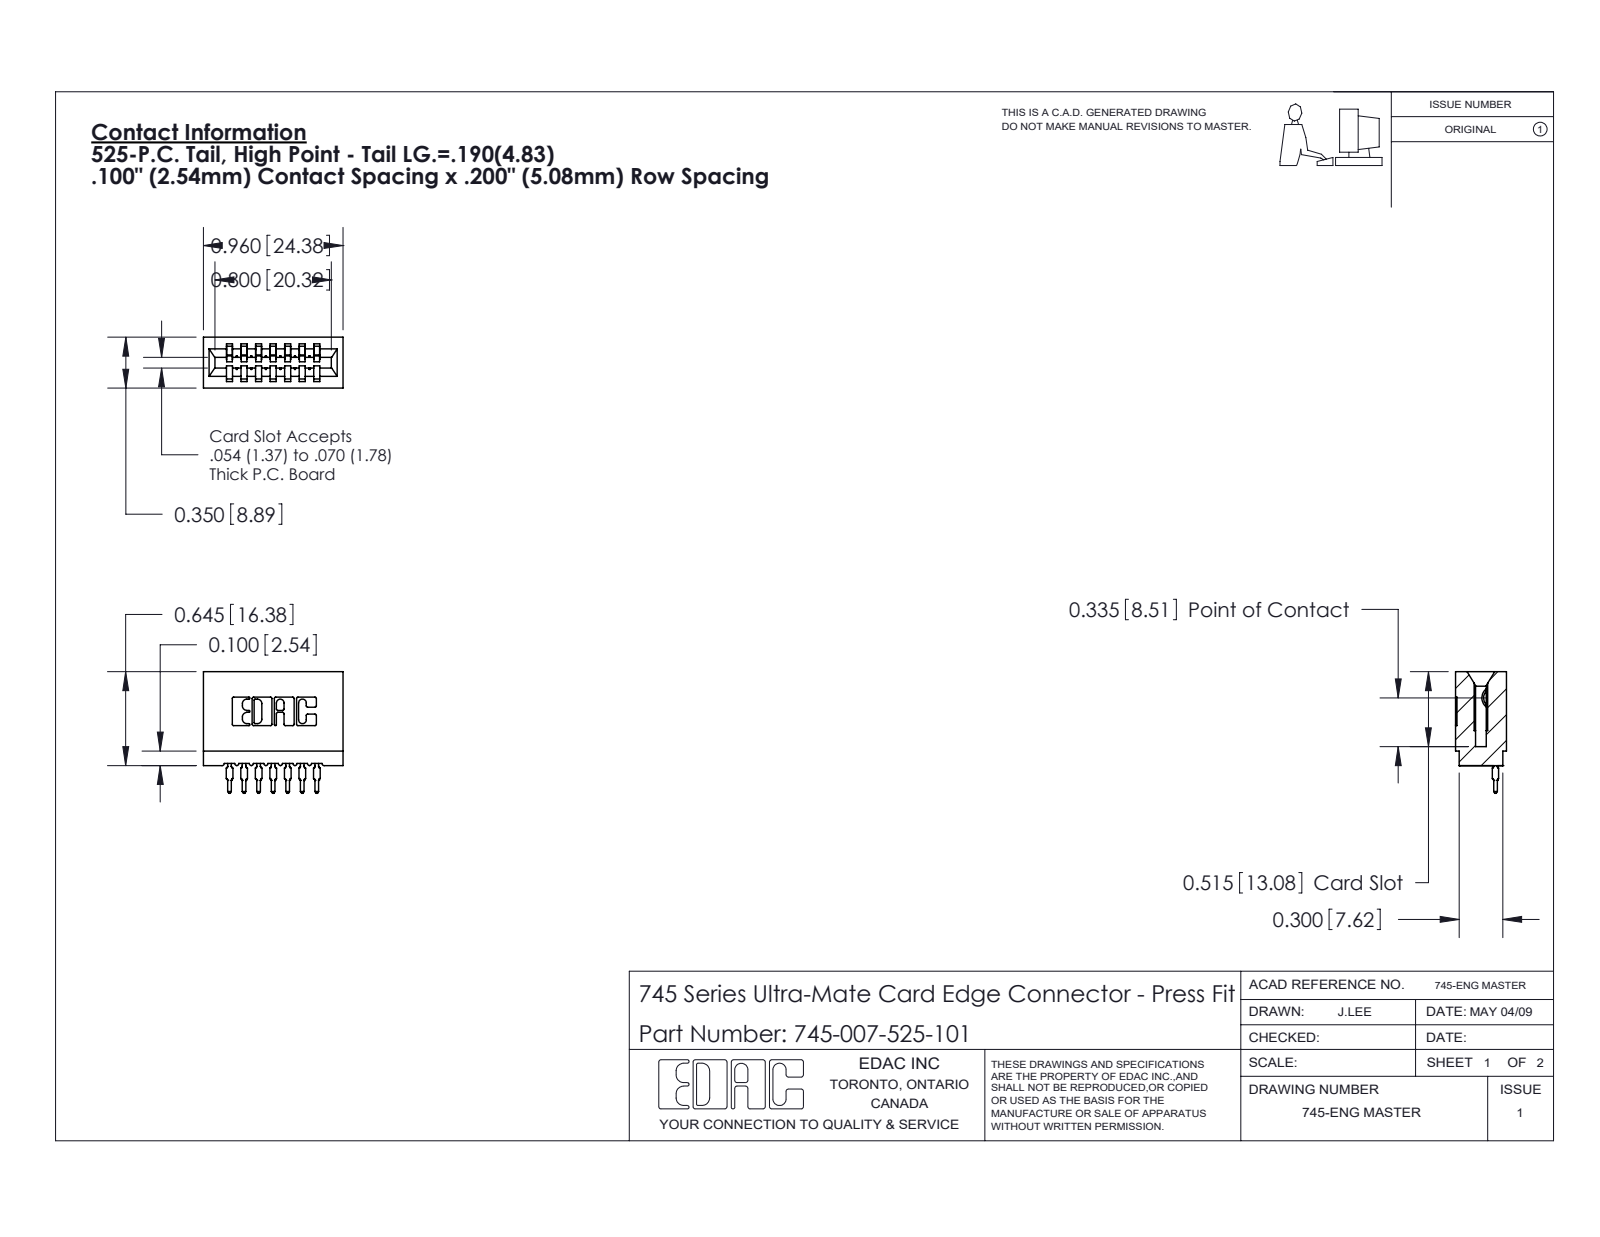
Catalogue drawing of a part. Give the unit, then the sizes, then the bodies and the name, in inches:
Units: inches
Overall size (bounding box): 0.96 × 0.836 × 0.35
Partial cylindrical surfaces — rounded edges, fillets, slot ends (radius × count): R0.01 ×22, R0.015 ×14, R0.021 ×14, R0.007 ×6, R0.031 ×6, R0.005 ×4, R0.011 ×4, R0.026 ×3
Main face-to-face distances: 0.1, 0.2, 0.3, 0.042, 0.058, 0.142, 0.4, 0.242, 0.158, 0.35
Volume: 0.143 in³ · Surface area: 5.658 in²
Bodies: 8 solids, 879 faces (524 planar, 173 cylindrical, 182 other)
Part name (STEP PRODUCT): 745 Part_Insulator Option - 01; 745-292-001_525; 745-007-525-101
STEP written by: SolidWorks 2020 (CONFIG_CONTROL_DESIGN)
